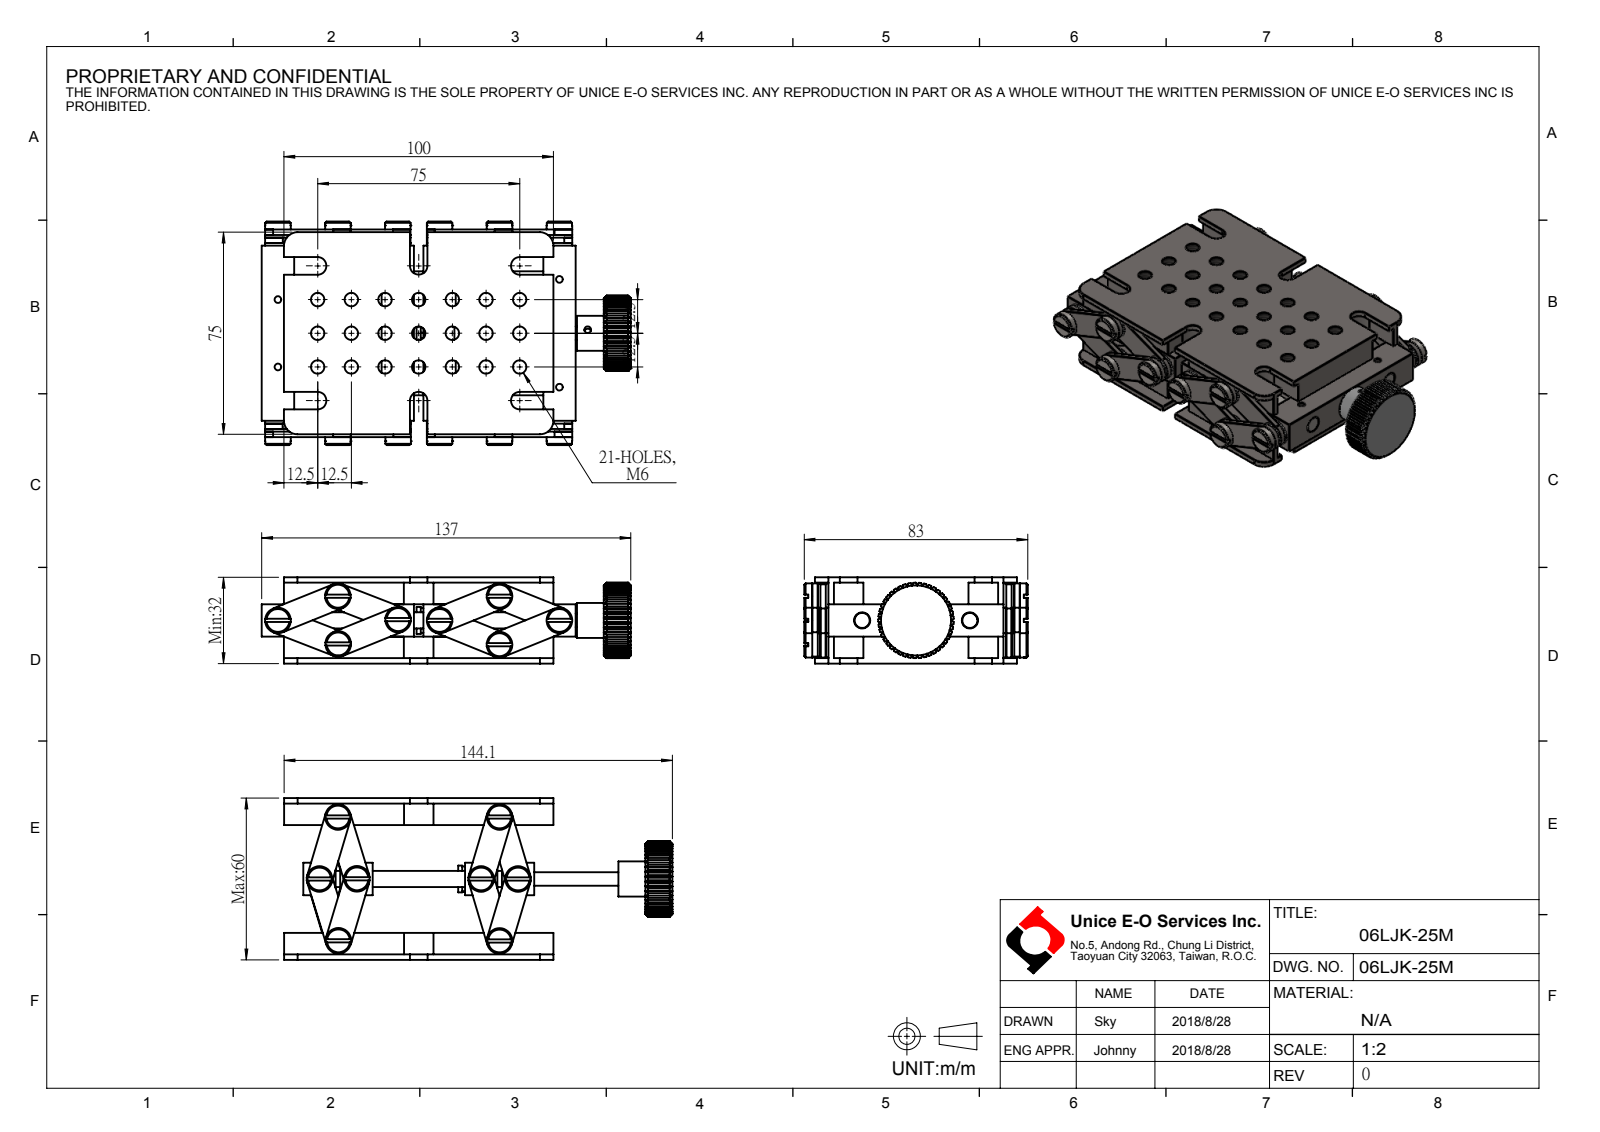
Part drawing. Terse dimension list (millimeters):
name: 06LJK-25M
written by: SolidWorks 2016 (AUTOMOTIVE_DESIGN)
unit: mm
bodies: 0 solids, 866 faces (389 planar, 341 cylindrical, 136 other)
size: 137 × 83 × 32
holes: 21× ⌀5, 5× ⌀2.5, 4× ⌀6, 1× ⌀11
bosses: 10× ⌀9.5, 1× ⌀13, 1× ⌀4
rounds: 6× R3.25, 6× R5.5, 4× R5, 1× R14
face distances: 22, 10, 12, 2, 3, 32, 72, 1, 8, 69
hole spacings: 12.5, 27.95, 17.68, 25, 39.53, 37.5, 51.54, 35.36
